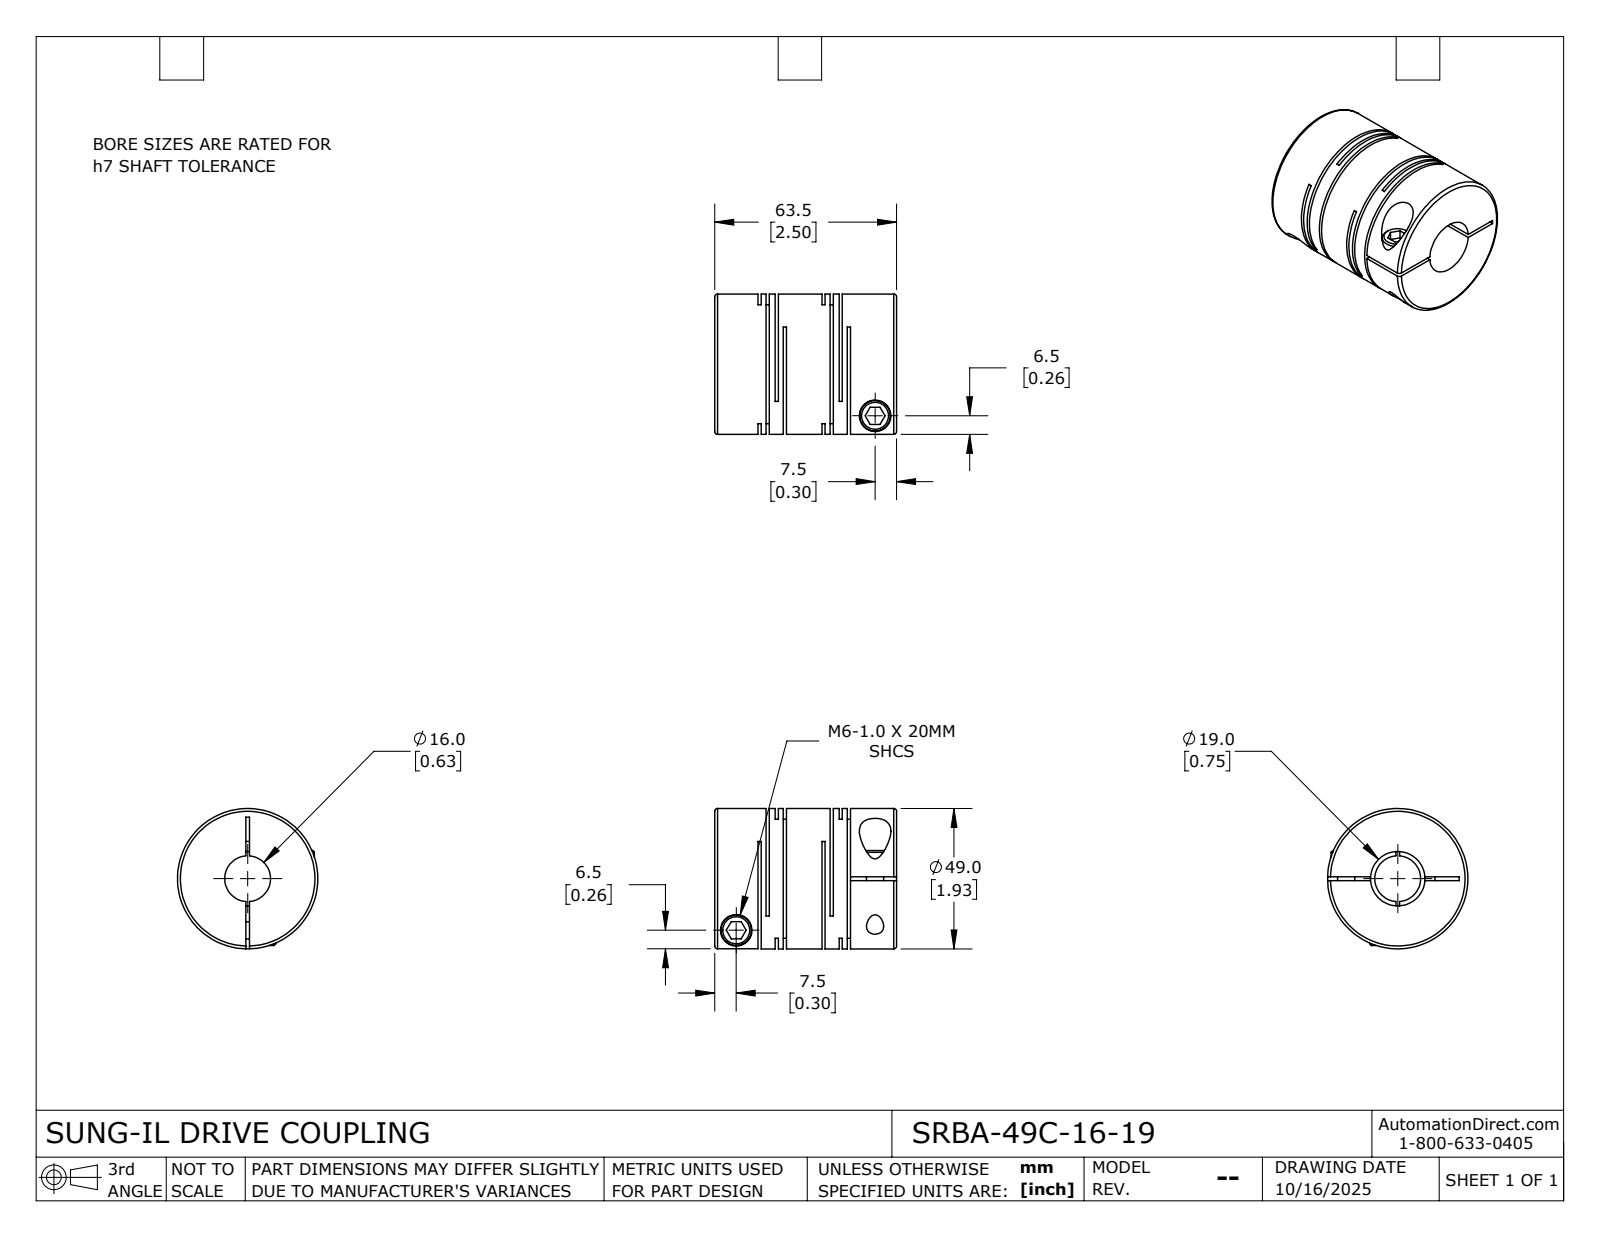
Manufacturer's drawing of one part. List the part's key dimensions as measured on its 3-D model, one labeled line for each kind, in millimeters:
Part name (STEP PRODUCT): SRBA-49C-16-19
STEP written by: SolidWorks 2024 (CONFIG_CONTROL_DESIGN)
Units: millimetres
Bodies: 1 solid, 115 faces (60 planar, 42 cylindrical, 13 other)
Overall size (bounding box): 63.5 × 49 × 49
Volume: 89 031 mm³ · Surface area: 38 517 mm²
Round holes (diameter × count): ⌀6 ×2, ⌀11 ×2, ⌀16 ×1, ⌀19 ×1
Round bosses / shafts (diameter × count): ⌀10.6 ×2, ⌀49 ×1
Main face-to-face distances: 6, 1.1, 22.35, 2.85, 21.25, 3.15, 1.75, 4.9, 19.5, 16.35
